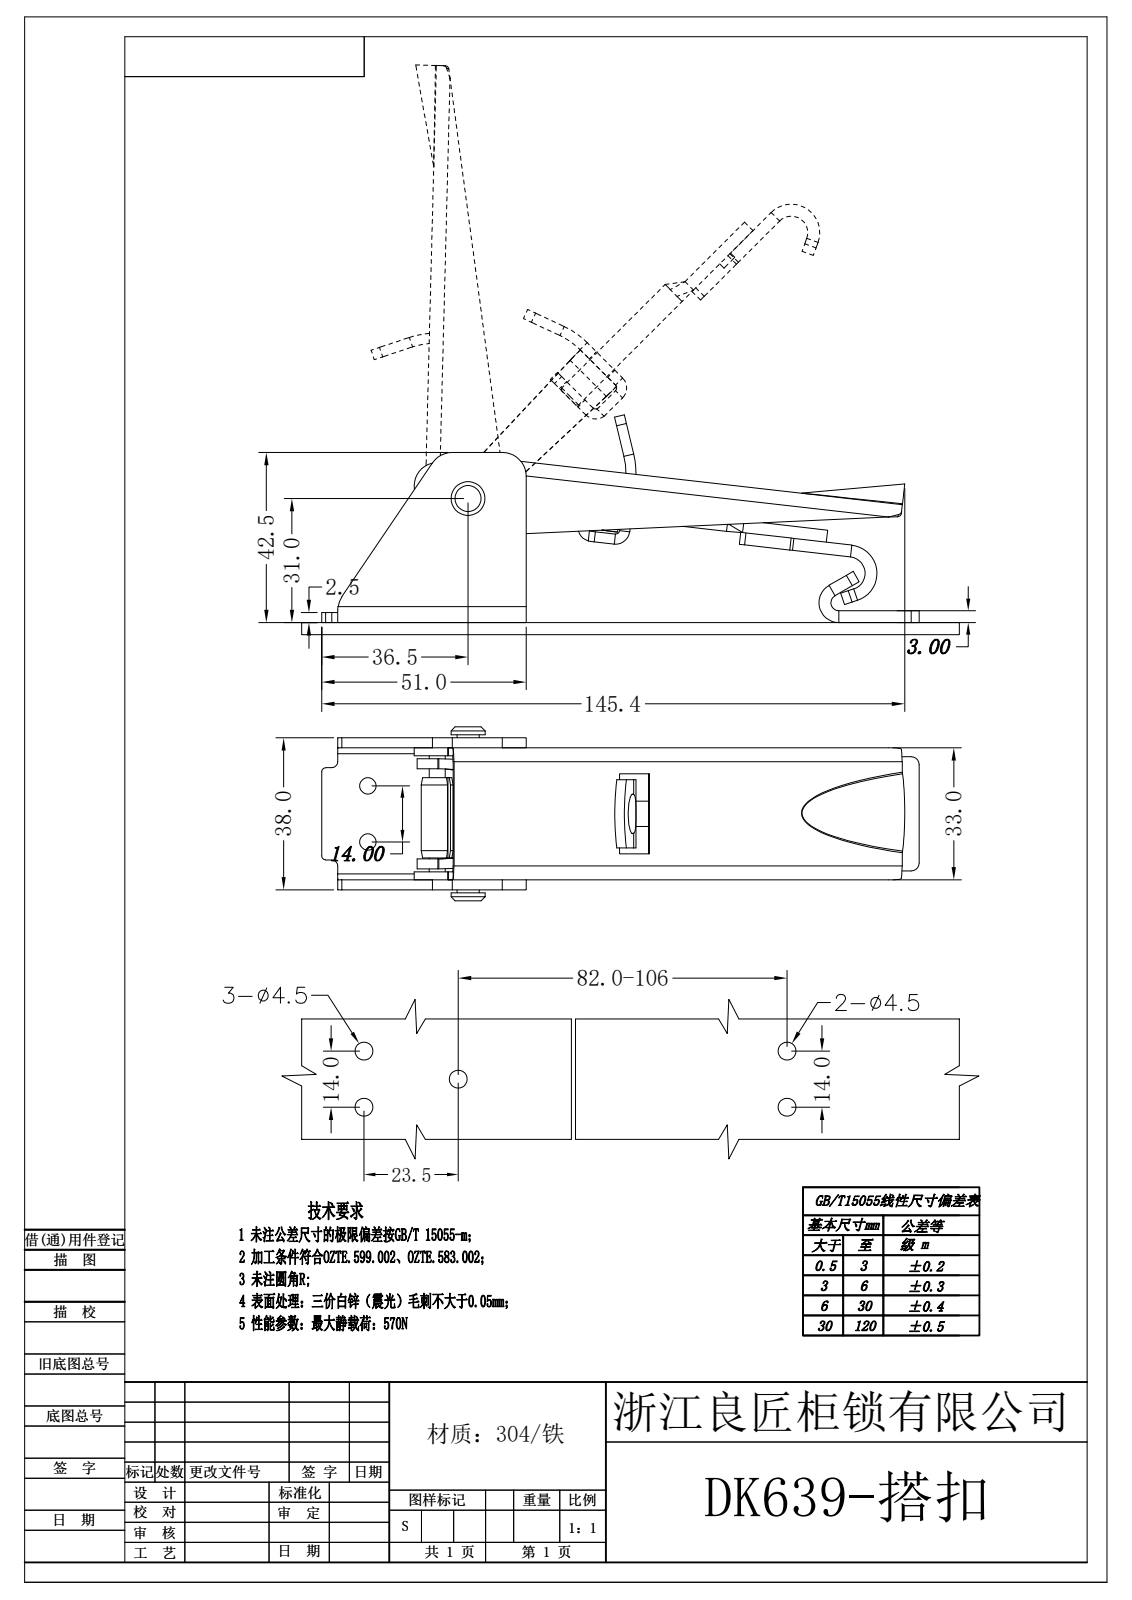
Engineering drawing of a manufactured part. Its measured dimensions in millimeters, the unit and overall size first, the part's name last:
Units: millimetres
Overall size (bounding box): 206.84 × 56.86 × 50
Round holes (diameter × count): ⌀4.5 ×5, ⌀4.2 ×3, ⌀4 ×2, ⌀6.5 ×2, ⌀7 ×2, ⌀5 ×1, ⌀5.19 ×1, ⌀5.7 ×1
Round bosses / shafts (diameter × count): ⌀8.5 ×1, ⌀8 ×1, ⌀6.35 ×1, ⌀5.5 ×1
Partial cylindrical surfaces — rounded edges, fillets, slot ends (radius × count): R2 ×11, R1.5 ×10, R1 ×4, R3.5 ×4, R4 ×4, R5 ×3, R6 ×3, R3.9 ×2
Main face-to-face distances: 5, 2.5, 2, 35.5, 6, 10.5, 33, 33.5, 8.5, 31
Hole centre spacings: 129.5, 0.5, 14, 14.5, 24.52, 106.23, 106.26, 130.25
Volume: 85 894 mm³ · Surface area: 59 866 mm²
Bodies: 14 solids, 327 faces (155 planar, 126 cylindrical, 46 other)
Part name (STEP PRODUCT): DK639; square nuts--product grade c gb_GB_SPECIAL_TYPE12 M6-N; spring pin slotted light duty1 gb_GB_PARALLEL_PINS_TYPE7 8X20
STEP written by: Rhino 8.5 (CONFIG_CONTROL_DESIGN)
